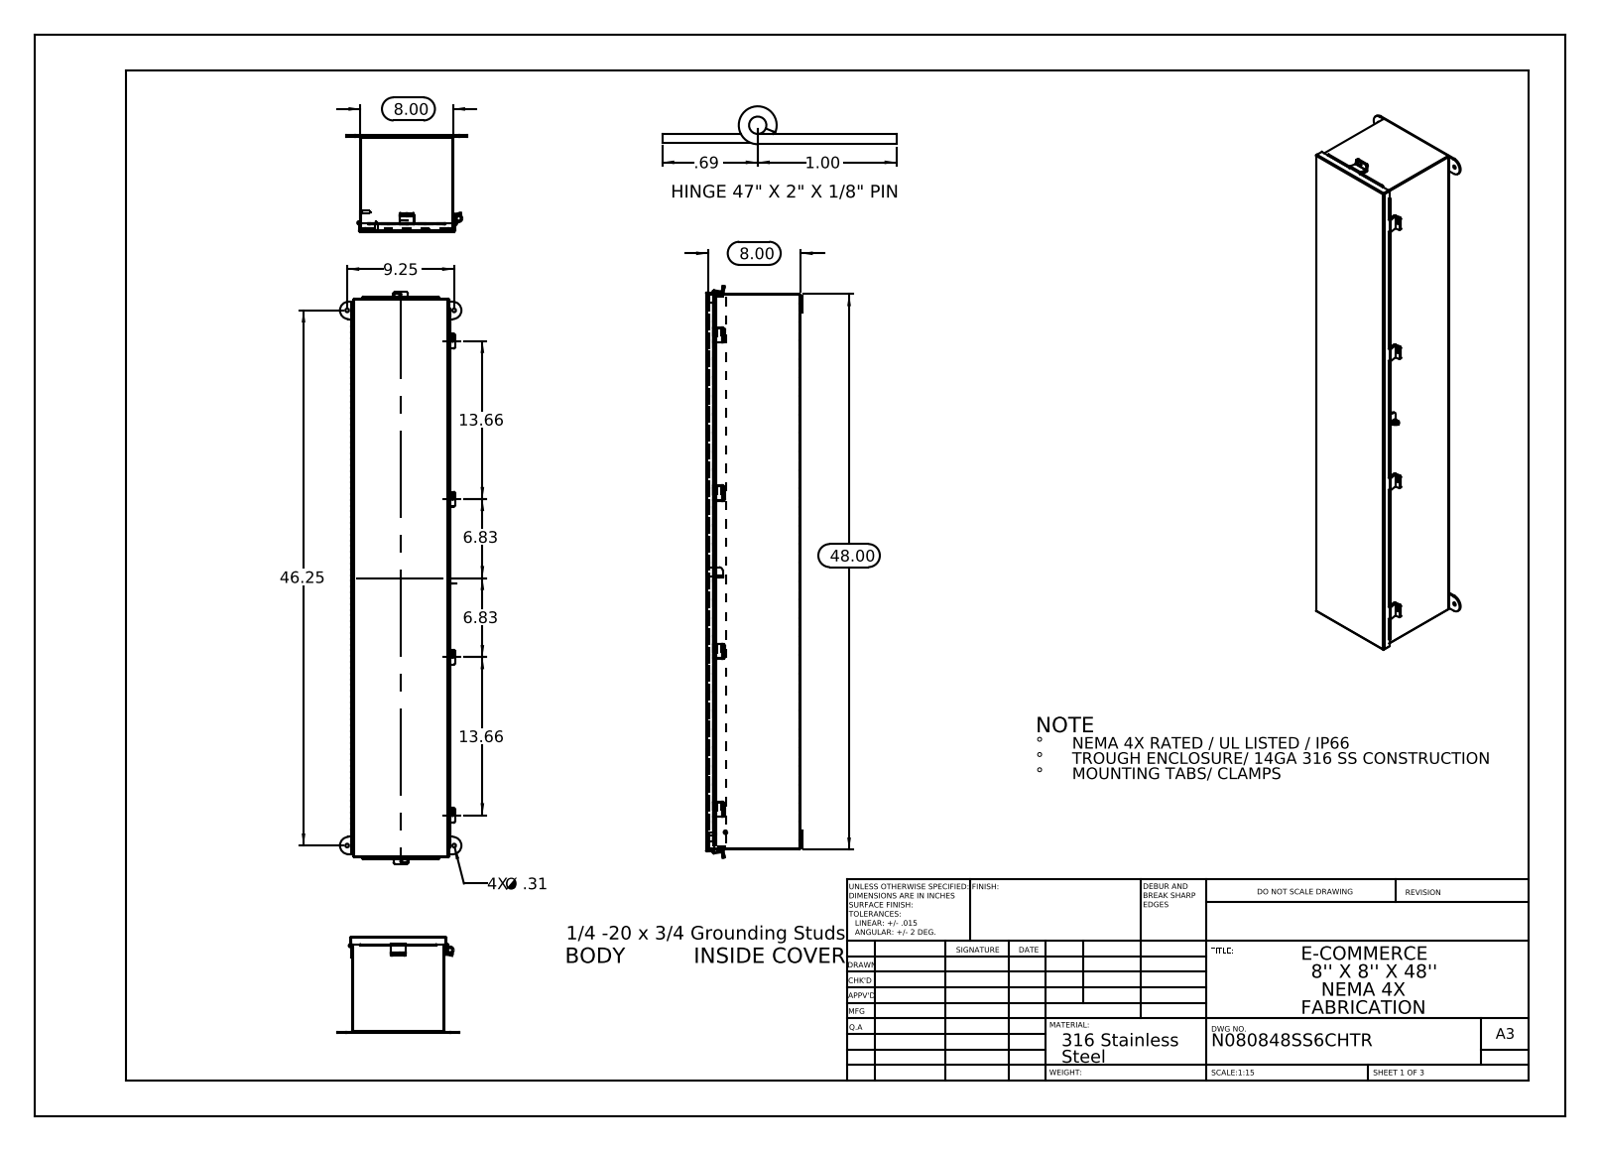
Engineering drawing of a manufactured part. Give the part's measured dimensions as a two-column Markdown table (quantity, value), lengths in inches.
| quantity | value |
| --- | --- |
| part name | N080848SSCHTR _JIC Hinge; N080848SSCHTR JIC_Cover_Template; N080848SSCHTR Hinge Body Side; N080848SSCHTR (+8 more) |
| STEP written by | SolidWorks 2013 (CONFIG_CONTROL_DESIGN) |
| units | inches |
| bodies | 23 solids, 1376 faces (825 planar, 531 cylindrical, 20 other) |
| overall size | 49.407 × 10.5 × 8.337 |
| volume | 144.8 in³ |
| surface area | 3 895 in² |
| round holes (diameter × count) | 0.25 × 6, 0.313 × 4, 0.125 × 1, 0.125 × 1, 0.375 × 1 |
| round bosses / shafts (diameter × count) | 0.315 × 2, 0.236 × 2, 0.273 × 1, 0.25 × 1 |
| partial cylindrical surfaces (radius × count) | 0.125 × 23, 0.009 × 12, 0.133 × 12, 0.013 × 10, 0.088 × 10, 0.083 × 6, 0.1 × 6, 0.75 × 4 |
| main face-to-face distances | 0.075, 7.925, 8.128, 8, 7.85, 8.203, 8.053, 0.149, 8.074, 47.925 |
| hole center spacings | 9.25, 13.66, 27.32, 46.25, 47.166, 8.635, 13.66, 40.98 |
